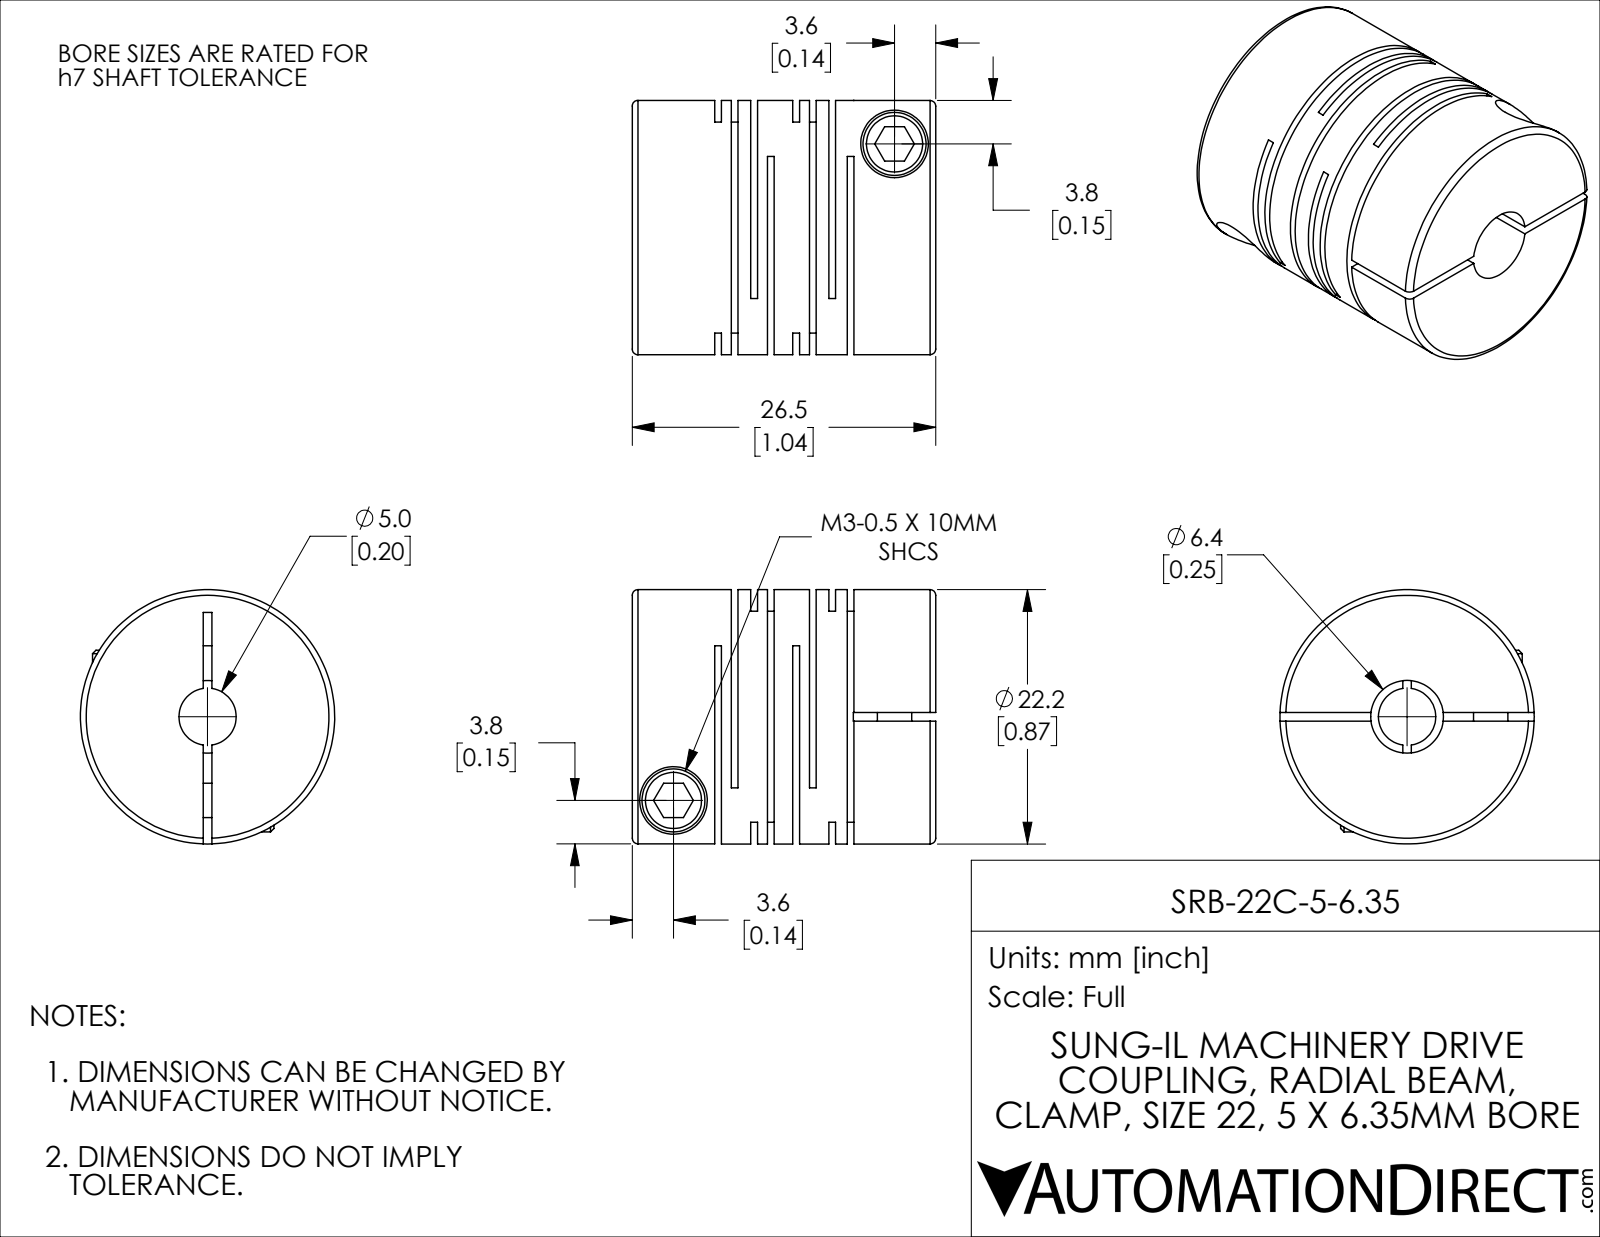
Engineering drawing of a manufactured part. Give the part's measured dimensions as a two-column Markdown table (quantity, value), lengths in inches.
| quantity | value |
| --- | --- |
| part name | SRB-22C-5-6 |
| STEP written by | SolidWorks 2021 (CONFIG_CONTROL_DESIGN) |
| units | inches |
| bodies | 1 solid, 115 faces (60 planar, 42 cylindrical, 13 other) |
| overall size | 1.043 × 0.874 × 0.874 |
| volume | 0.478 in³ |
| surface area | 12.68 in² |
| round holes (diameter × count) | 0.118 × 2, 0.232 × 2, 0.197 × 1, 0.236 × 1 |
| round bosses / shafts (diameter × count) | 0.217 × 2, 0.874 × 1 |
| main face-to-face distances | 0.023, 0.269, 0.124, 0.057, 0.211, 0.067, 0.144, 0.08, 0.292, 0.245 |
